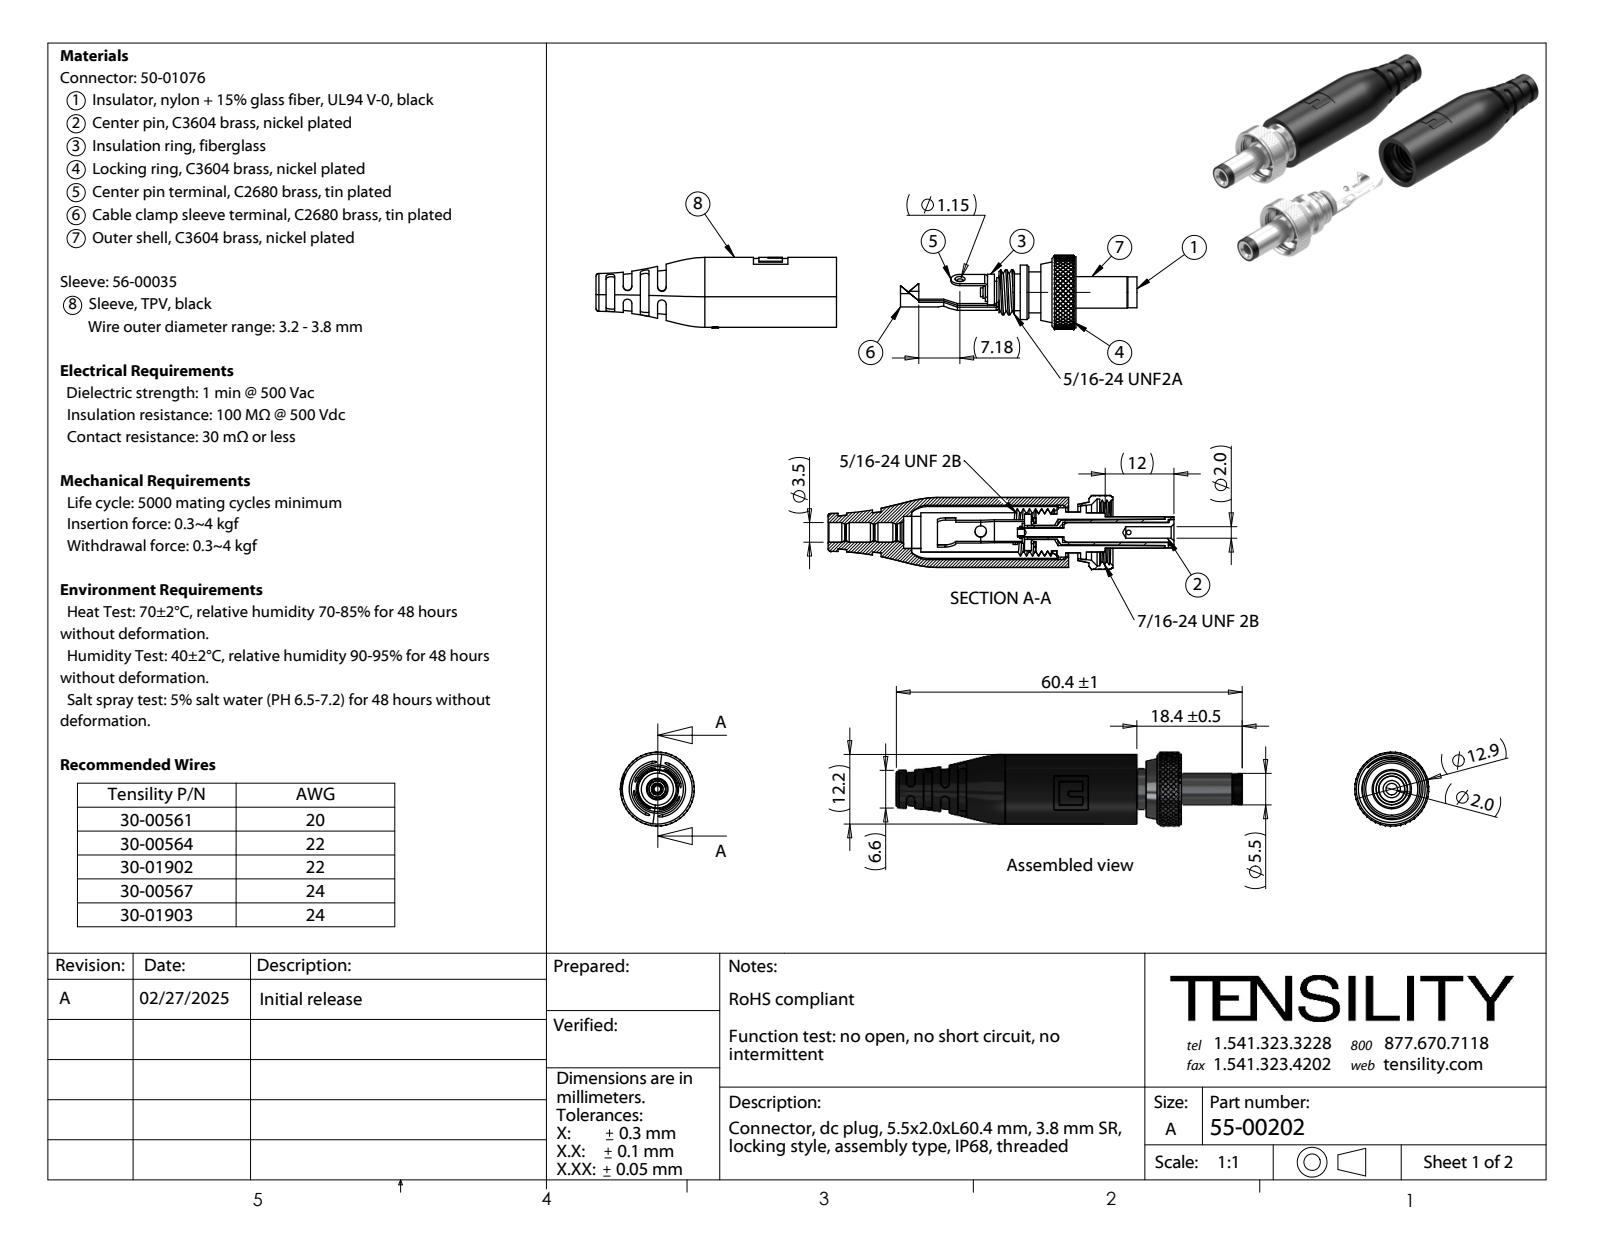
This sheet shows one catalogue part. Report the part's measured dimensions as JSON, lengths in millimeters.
{"part_name": "50-01076_Center pin terminal; 50-01076_Outer tube; 50-01076_Tip insulator; 50-01076_Glass fiber (+6 more)", "step_written_by": "SolidWorks 2021 (CONFIG_CONTROL_DESIGN)", "units": "millimeters", "bodies": {"solids": 8, "faces": 368, "planar": 124, "cylindrical": 131, "other": 113}, "overall_size": [60.9, 12.9, 12.9], "volume_mm3": 2693, "surface_area_mm2": 5562, "round_holes": [[1.15, 2], [0.8, 1], [1.6, 1], [2, 1], [2.01, 1], [2.45, 1], [2.5, 1], [3.35, 1], [3.55, 1], [4.55, 1], [4.6, 1], [9.5, 1]], "round_bosses_or_shafts": [[12.9, 1], [12.4, 1], [12.2, 1], [7.85, 1], [7.15, 1], [6.85, 1], [6.4, 1], [5.5, 1]], "partial_cylinders_radius": [[0.75, 8], [0.2, 4], [1.57, 2], [6.1, 2], [0.1, 1], [0.4, 1], [0.5, 1], [0.6, 1]], "face_to_face_distances": [1.5, 0.4, 5.2, 4.1, 29.75, 3.7, 3.6, 33.35, 9.25, 4.5]}
